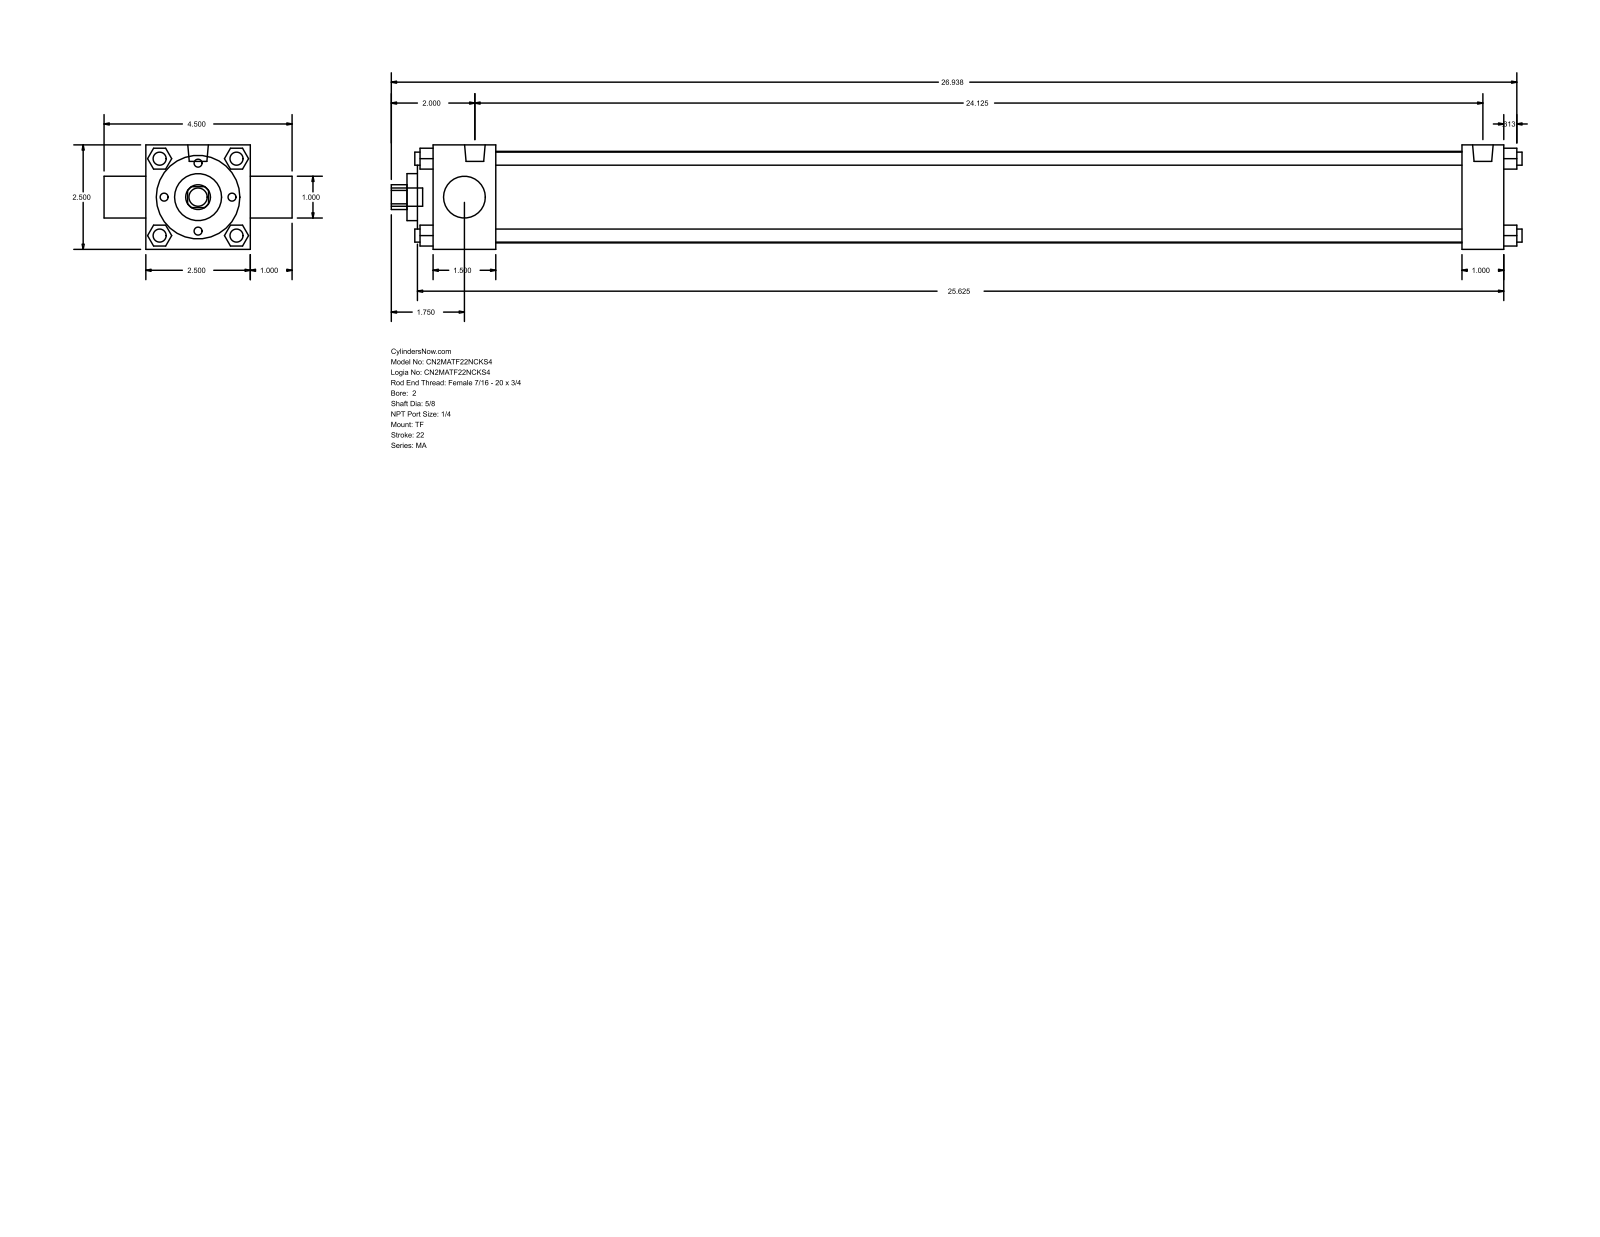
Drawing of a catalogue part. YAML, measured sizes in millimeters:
part_name: "MA_TF__0200_0.625"
step_written_by: "GSSL Pune (CONFIG_CONTROL_DESIGN)"
units: millimeters
bodies: {solids: 0, faces: 122, planar: 93, cylindrical: 29, other: 0}
overall_size: [687.39, 114.3, 63.5]
round_holes:
  - {diameter: 15.88, count: 1}
  - {diameter: 25.4, count: 1}
  - {diameter: 28.57, count: 1}
  - {diameter: 50.8, count: 1}
  - {diameter: 55.63, count: 1}
round_bosses_or_shafts:
  - {diameter: 7.94, count: 7}
  - {diameter: 12.49, count: 2}
  - {diameter: 11.11, count: 1}
partial_cylinders:
  - {radius: 7.54, count: 1}
face_to_face_distances: [63.5, 38.1, 12.7, 9.52, 650.87, 625.48, 587.38, 612.77, 25.39, 47.62]
